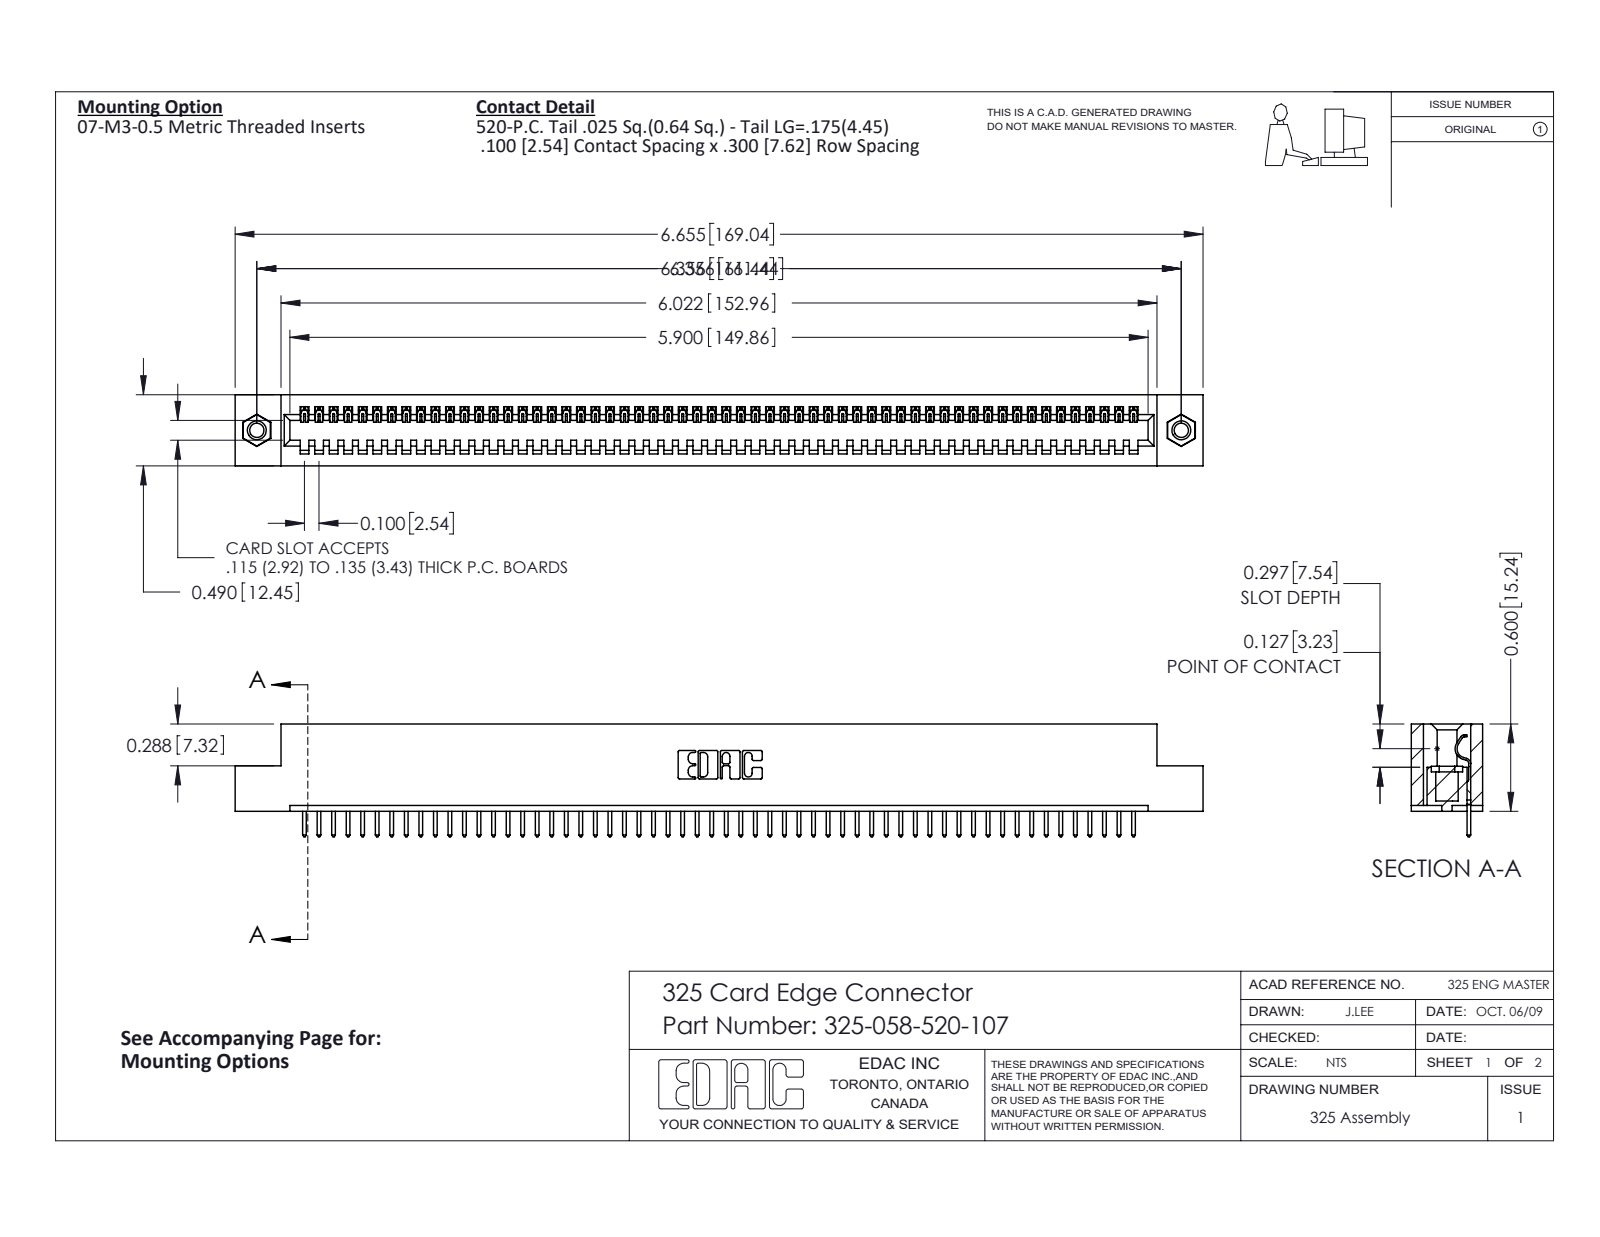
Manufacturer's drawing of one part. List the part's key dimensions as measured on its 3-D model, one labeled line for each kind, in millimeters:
Part name (STEP PRODUCT): 345-250-001_345-250-005-103; 325-292-001_325-293-120; 325 Part_TI; 325-058-520-107
STEP written by: SolidWorks 2016 (CONFIG_CONTROL_DESIGN)
Units: millimetres
Bodies: 61 solids, 3538 faces (2538 planar, 984 cylindrical, 16 other)
Overall size (bounding box): 169 × 19.7 × 12.4
Volume: 21 420 mm³ · Surface area: 23 090 mm²
Round holes (diameter × count): ⌀2.5 ×2, ⌀3.2 ×2, ⌀4.1 ×2
Round bosses / shafts (diameter × count): ⌀3.9 ×2
Partial cylindrical surfaces — rounded edges, fillets, slot ends (radius × count): R0.2 ×116, R0.3 ×116, R0.3 ×22, R0.2 ×6, R0.8 ×6, R0.7 ×3, R0.4 ×1, R0.6 ×1
Main face-to-face distances: 2.1, 10.3, 12.4, 2.7, 9.7, 0.6, 7.6, 8.3, 6.7, 14.2
Hole centre spacings: 161.4
